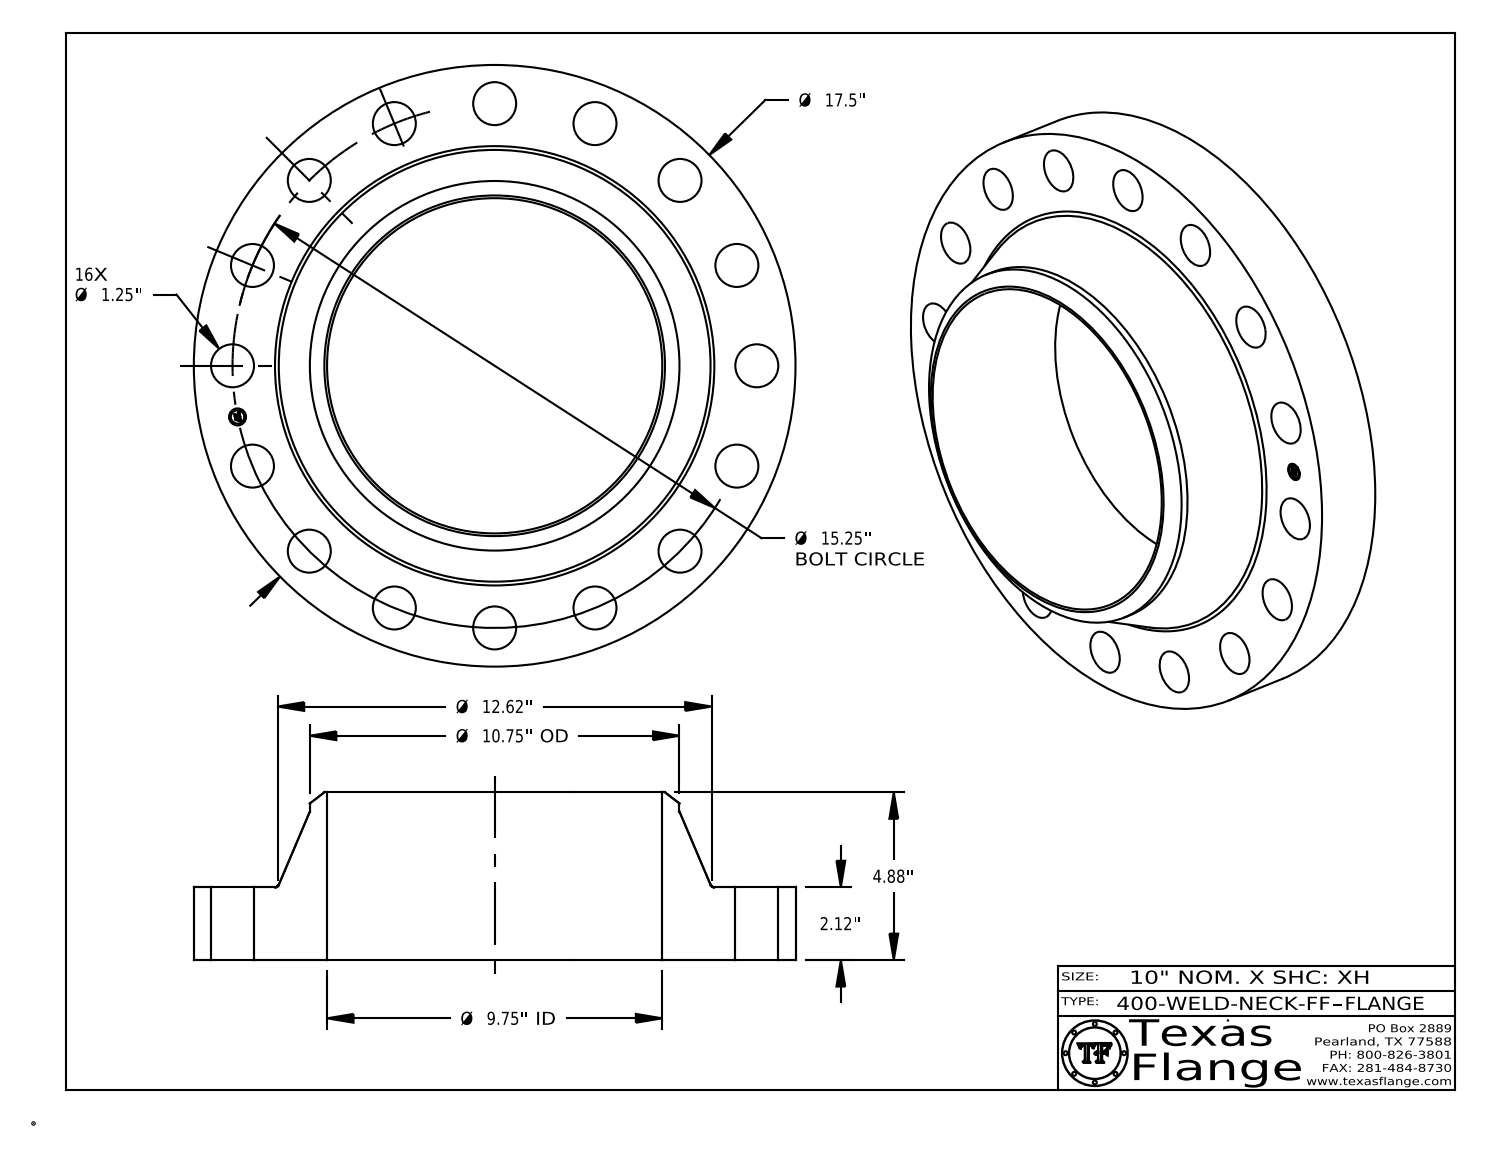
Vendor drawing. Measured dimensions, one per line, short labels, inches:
name: 400-WELD-NECK-FF
written by: CATIA V5 STEP AP214 (AUTOMOTIVE_DESIGN)
unit: in
bodies: 1 solid, 432 faces (368 planar, 58 cylindrical, 6 other)
size: 17.5 × 17.5 × 4.88
volume: 389 in³; area: 756 in²
holes: 16× ⌀1.25, 1× ⌀0.495, 1× ⌀9.75
bosses: 8× ⌀0.03, 1× ⌀17.5, 1× ⌀10.75, 1× ⌀0.39
face distances: 2.12, 4.88, 2.76, 0.015, 2.105, 2.775, 0.148, 0.145, 0.027, 0.096
hole spacings: 8.472, 10.783, 14.957, 14.089, 7.625, 2.975, 2.975, 5.836
